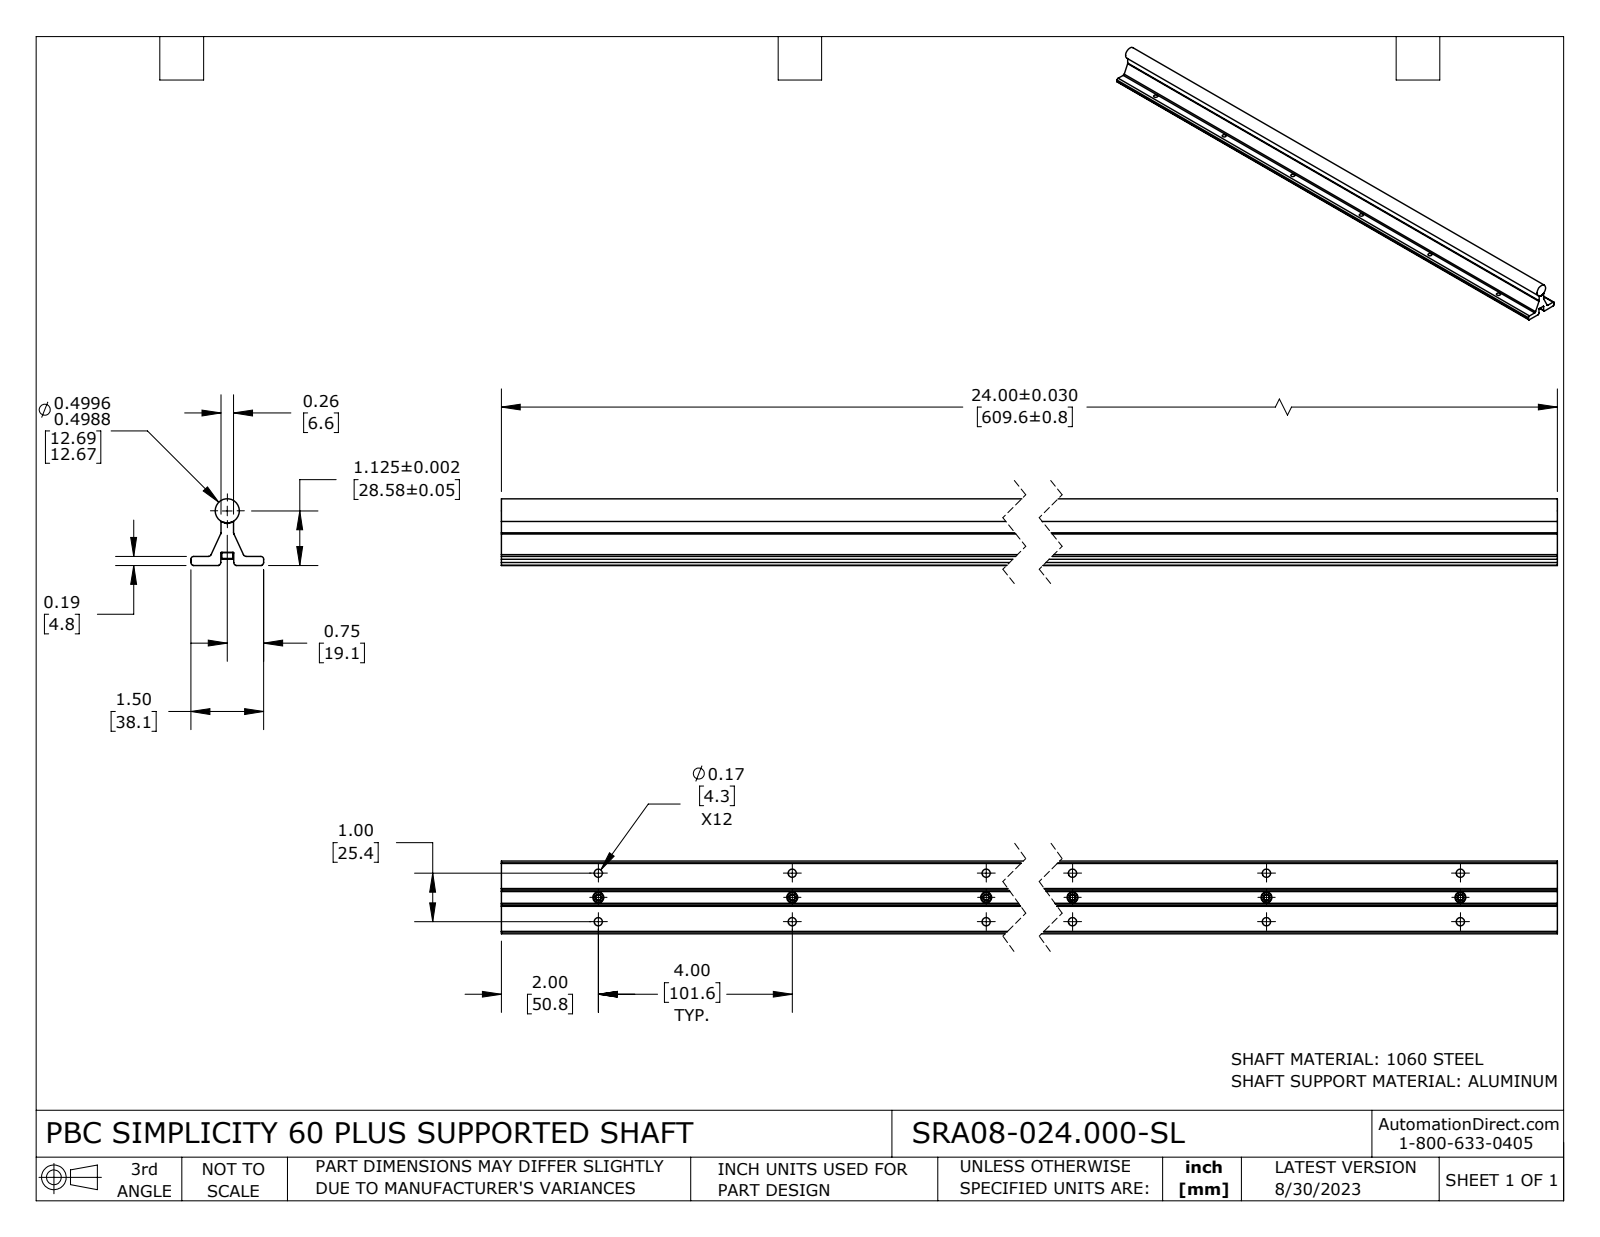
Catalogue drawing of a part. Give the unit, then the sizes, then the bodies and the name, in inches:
Units: inches
Overall size (bounding box): 24 × 1.5 × 1.375
Round holes (diameter × count): ⌀0.17 ×18, ⌀0.116 ×6, ⌀0.156 ×6
Round bosses / shafts (diameter × count): ⌀0.226 ×6, ⌀0.138 ×6, ⌀0.5 ×1
Partial cylindrical surfaces — rounded edges, fillets, slot ends (radius × count): R0.06 ×8, R0.015 ×2, R0.062 ×1, R0.063 ×1
Main face-to-face distances: 0.187, 0.27, 0.265, 0.083, 0.26, 0.615, 0.62, 0.88, 0.885, 1.5
Hole centre spacings: 4.031, 8.016, 4, 0.5, 8, 12.01, 4.123, 12
Volume: 16.38 in³ · Surface area: 162.3 in²
Bodies: 8 solids, 281 faces (93 planar, 98 cylindrical, 90 other)
Part name (STEP PRODUCT): SRA08-024.000-SL
STEP written by: SolidWorks 2021 (CONFIG_CONTROL_DESIGN)
